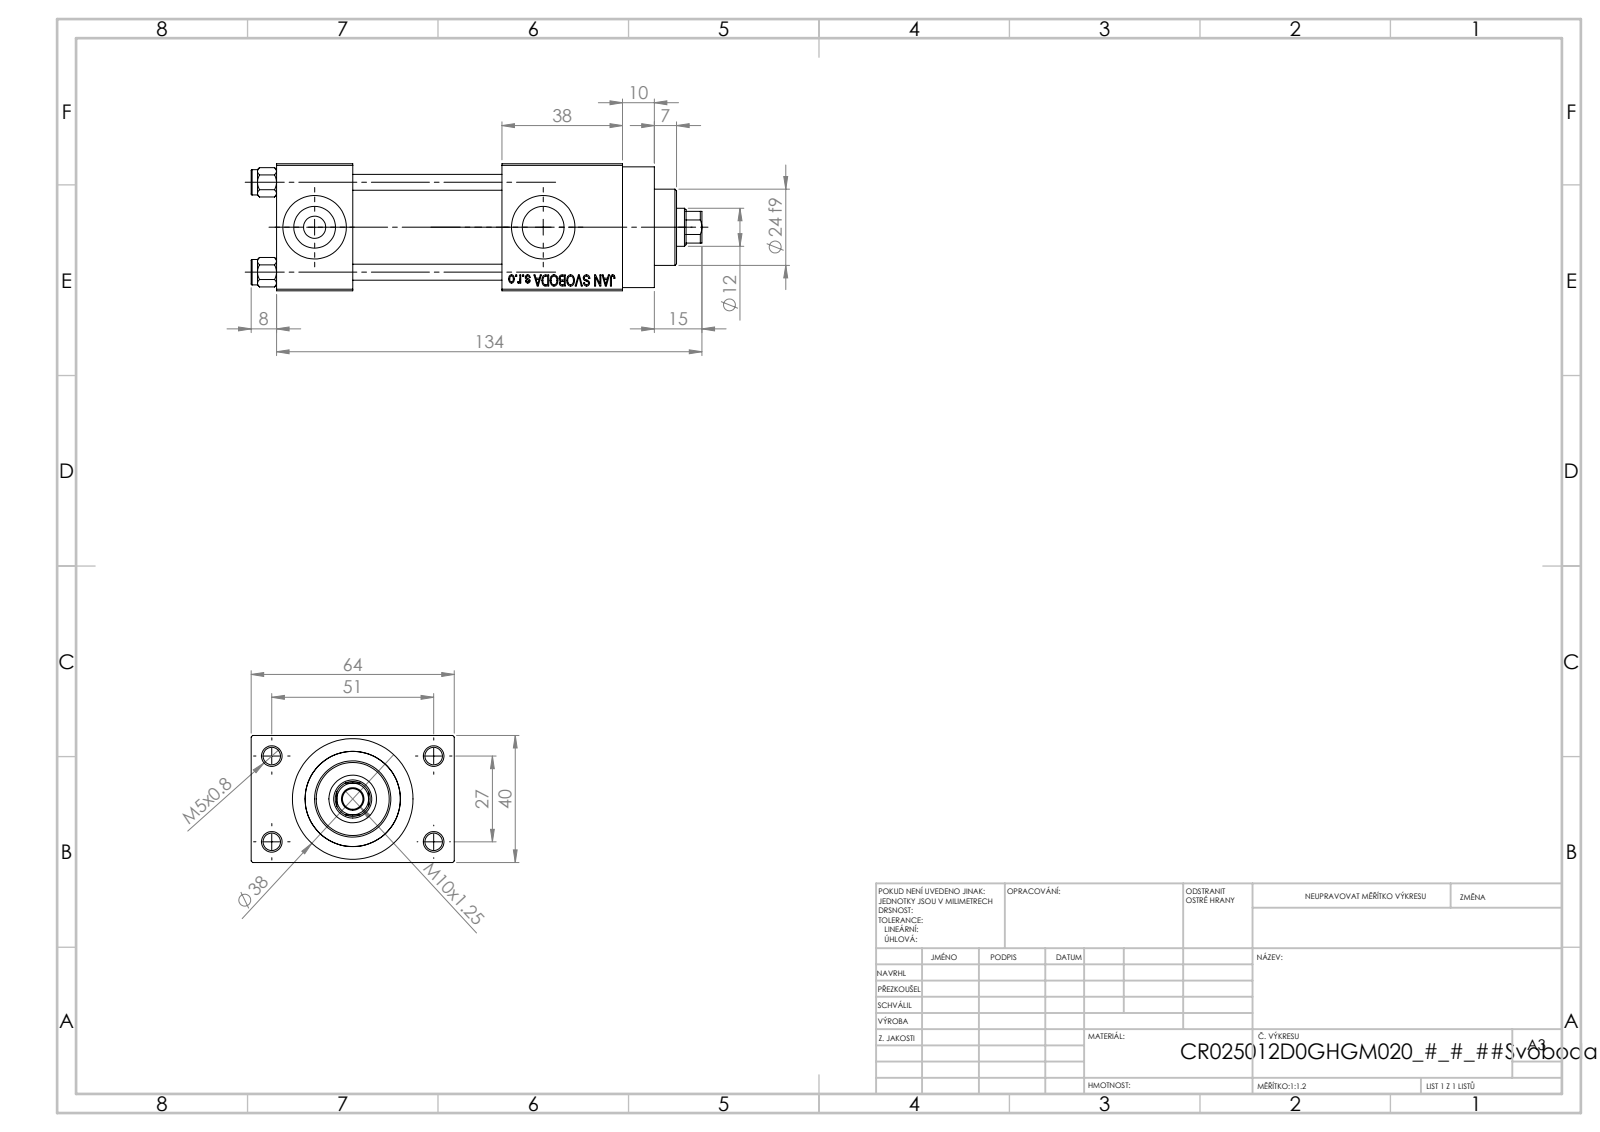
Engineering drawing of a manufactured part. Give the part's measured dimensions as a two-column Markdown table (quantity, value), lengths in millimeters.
| quantity | value |
| --- | --- |
| part name | V215CR_VCP_D; V215CR_D_Body; NUT_M5_D; V215_VC_A (+1 more) |
| STEP written by | SolidWorks 2019 (CONFIG_CONTROL_DESIGN) |
| units | millimeters |
| bodies | 11 solids, 1102 faces (496 planar, 88 cylindrical, 518 other) |
| overall size | 142 × 64 × 40 |
| volume | 173 683 mm³ |
| surface area | 62 160 mm² |
| round holes (diameter × count) | 5 × 4, 5.5 × 4, 20 × 3, 7 × 2, 13.16 × 2, 6.5 × 1, 12 × 1, 15 × 1, 25 × 1, 30 × 1 |
| round bosses / shafts (diameter × count) | 8 × 4, 38 × 1, 31 × 1, 24 × 1 |
| partial cylindrical surfaces (radius × count) | 5.5 × 1 |
| main face-to-face distances | 40, 12, 47, 24, 71, 52, 38, 109, 85, 64 |
| hole center spacings | 11.37, 20.01, 28.3, 28.85, 29.89, 39.66, 48.34, 27 |
